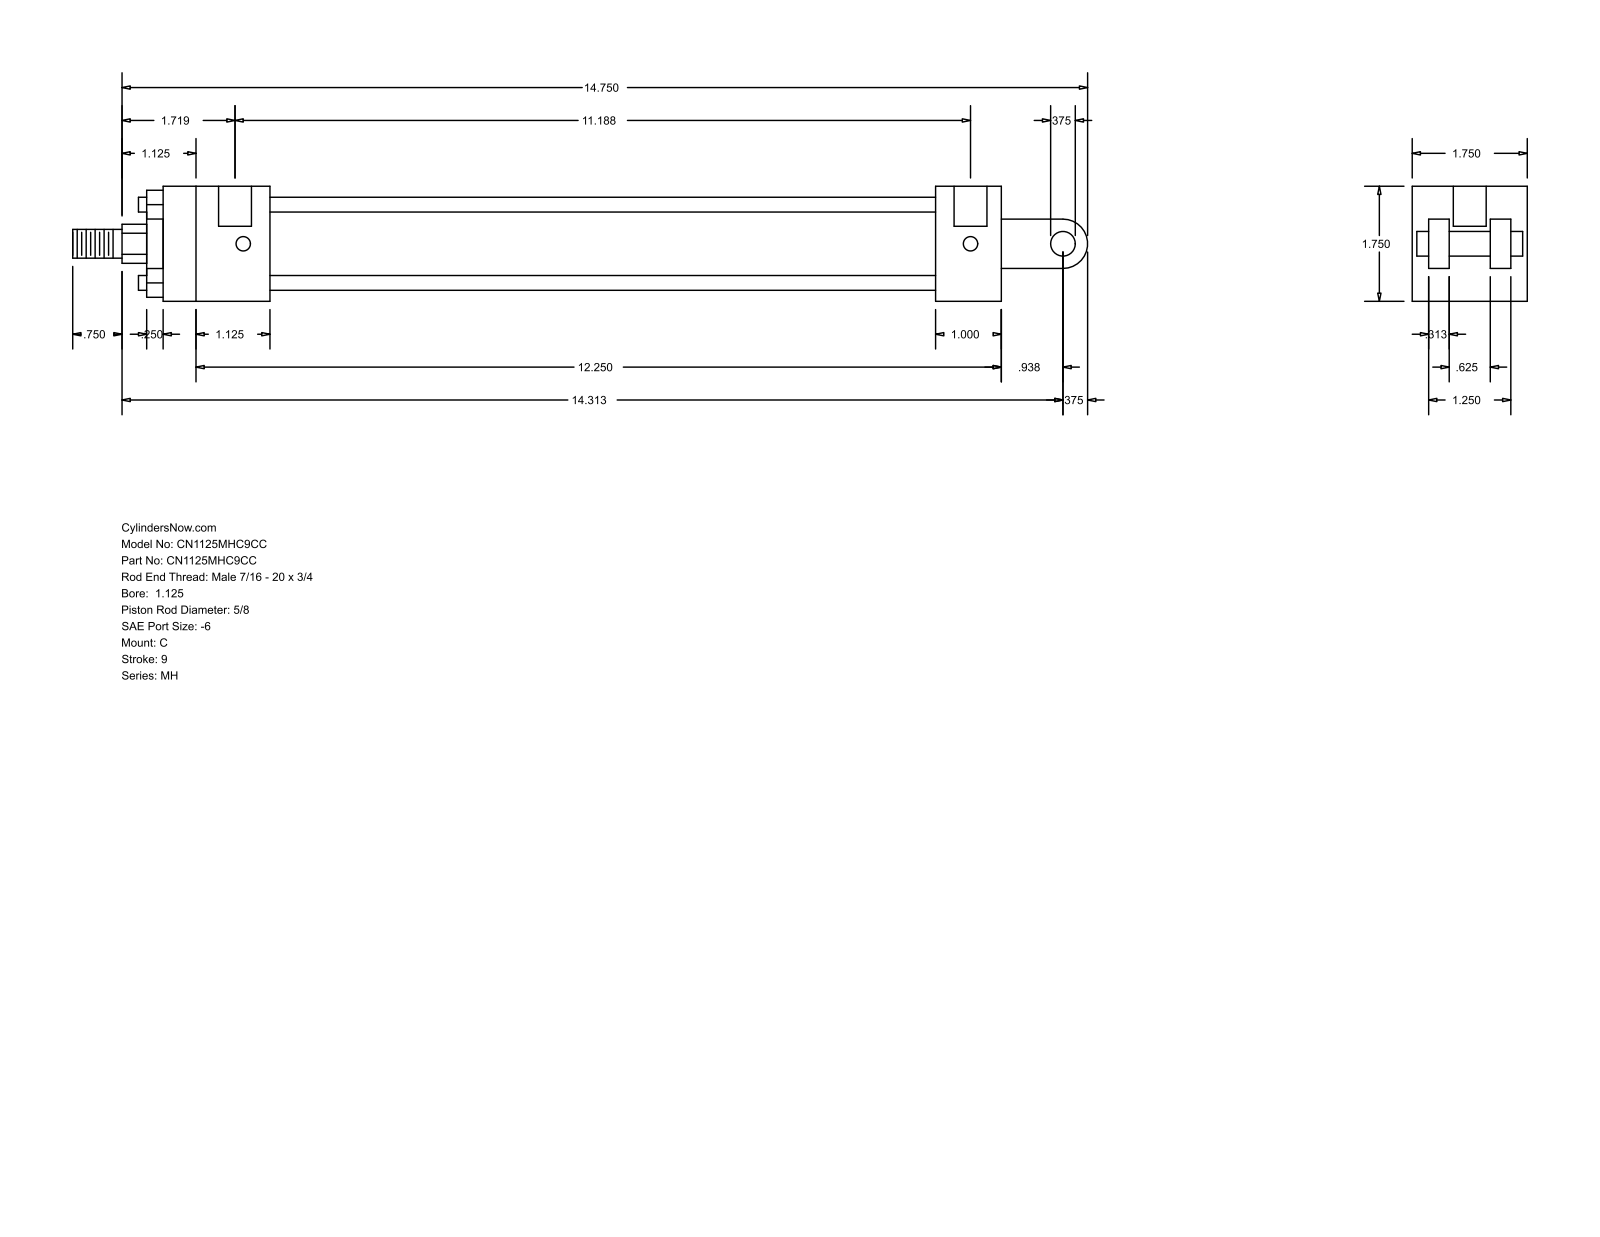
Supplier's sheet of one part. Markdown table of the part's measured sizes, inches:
| quantity | value |
| --- | --- |
| part name | MH_C__0112_0.625 |
| STEP written by | GSSL Pune (CONFIG_CONTROL_DESIGN) |
| units | inches |
| bodies | 0 solids, 99 faces (70 planar, 29 cylindrical, 0 other) |
| overall size | 15.437 × 1.75 × 1.75 |
| round holes (diameter × count) | 0.219 × 4, 0.5 × 2 |
| round bosses / shafts (diameter × count) | 0.225 × 4, 1.375 × 1, 1.125 × 1, 0.625 × 1, 0.437 × 1, 0.375 × 1 |
| partial cylindrical surfaces (radius × count) | 0.297 × 1, 0.375 × 1 |
| main face-to-face distances | 1.75, 0.25, 1.25, 0.563, 1.188, 1.5, 0.313, 0.938, 0.5, 1.625 |
| hole center spacings | 11.063, 0.125, 11.187 |
